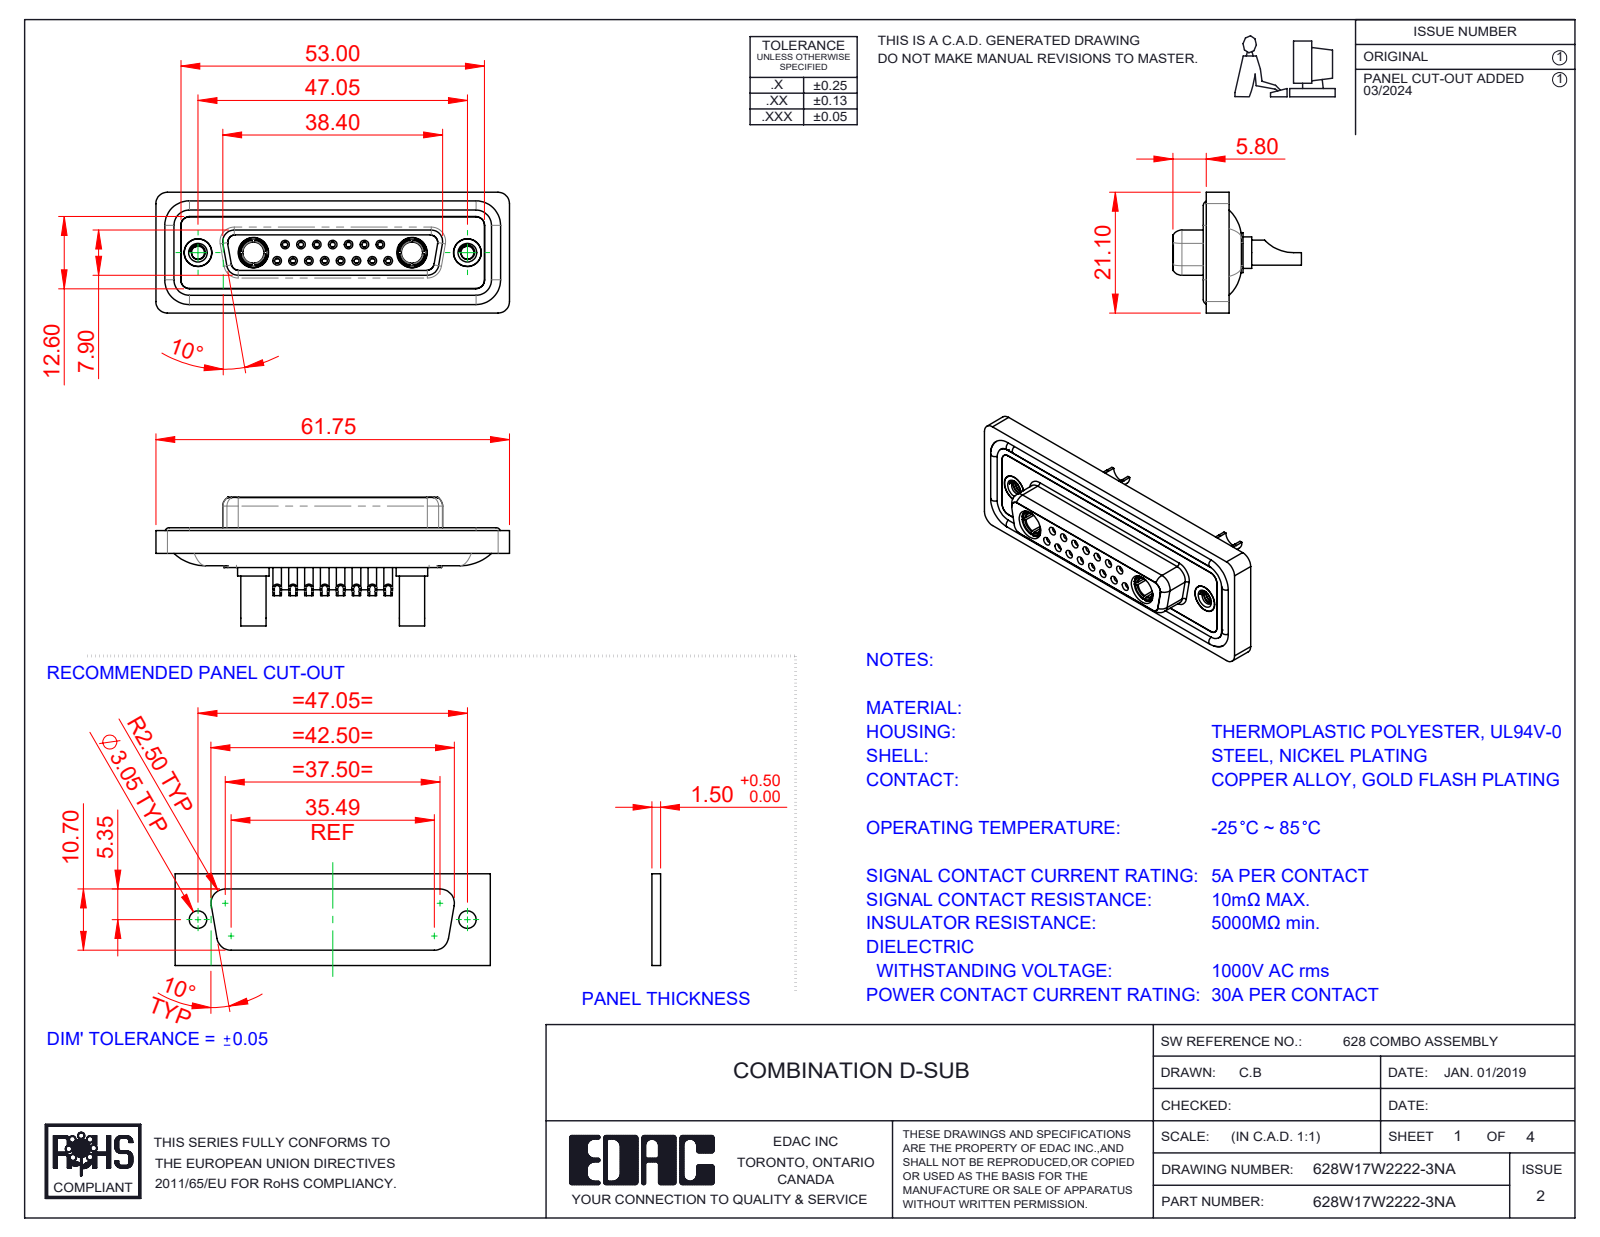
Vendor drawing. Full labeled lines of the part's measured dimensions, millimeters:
Part name (STEP PRODUCT): 628W17W2222-3NA; 628Combo Shell Front_25 Contacts; 628Combo Contact Row 1_22; 628Combo Threaded Rivet_A (+5 more)
STEP written by: SolidWorks 2023 (CONFIG_CONTROL_DESIGN)
Units: millimetres
Bodies: 26 solids, 1369 faces (424 planar, 557 cylindrical, 388 other)
Overall size (bounding box): 61.75 × 22.45 × 21.1
Volume: 8 405 mm³ · Surface area: 14 228 mm²
Round holes (diameter × count): ⌀0.9 ×15, ⌀1 ×15, ⌀1.1 ×15, ⌀1.5 ×15, ⌀2 ×15, ⌀1.6 ×8, ⌀1.7 ×7, ⌀4.85 ×4, ⌀2.26 ×2, ⌀3.5 ×2, ⌀3.7 ×2, ⌀4 ×2
Round bosses / shafts (diameter × count): ⌀2.2 ×15, ⌀1.6 ×11, ⌀5.5 ×2, ⌀5.2 ×2, ⌀4.96 ×2, ⌀4.95 ×2, ⌀4.8 ×2, ⌀4.75 ×2
Partial cylindrical surfaces — rounded edges, fillets, slot ends (radius × count): R1.5 ×22, R2 ×18, R1.35 ×8, R1.6 ×8, R1 ×6, R0.25 ×4, R0.5 ×4, R0.6 ×4
Main face-to-face distances: 0.4, 1.8, 7.45, 5.65, 6.6, 0.5, 7.05, 1.6, 2.9, 1.1
Hole centre spacings: 3.16, 2.77, 8.31, 5.54, 5.03, 5.04, 7.49, 11.08
